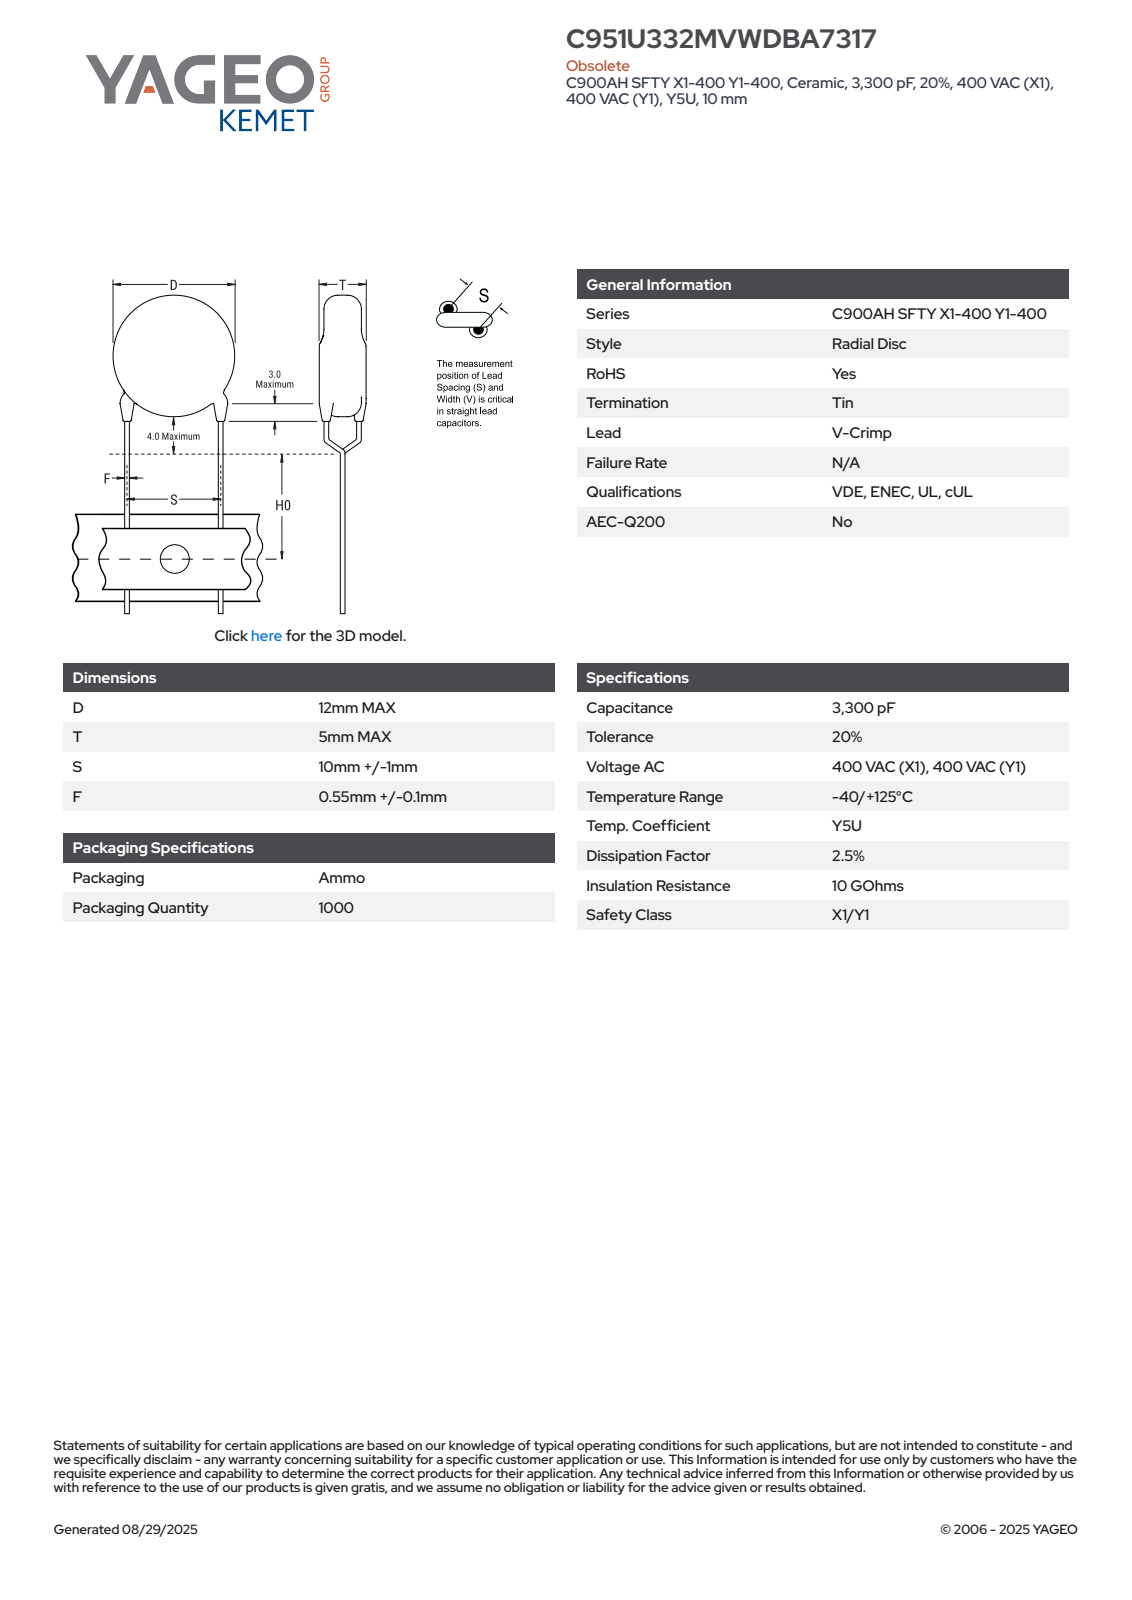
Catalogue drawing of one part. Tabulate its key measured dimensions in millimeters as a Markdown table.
| quantity | value |
| --- | --- |
| part name | CCD_VCC900_D12T5S10LL20F0.65 |
| STEP written by | SolidWorks 2014 (AUTOMOTIVE_DESIGN) |
| units | millimeters |
| bodies | 5 solids, 93 faces (65 planar, 16 cylindrical, 12 other) |
| overall size | 35.8 × 12 × 5 |
| volume | 570 mm³ |
| surface area | 507 mm² |
| round bosses / shafts (diameter × count) | 0.65 × 6, 12 × 1 |
| main face-to-face distances | 5, 22.9, 30.58, 7.68, 29.02, 6.12, 1.56, 0.42, 0.38, 1.26 |
